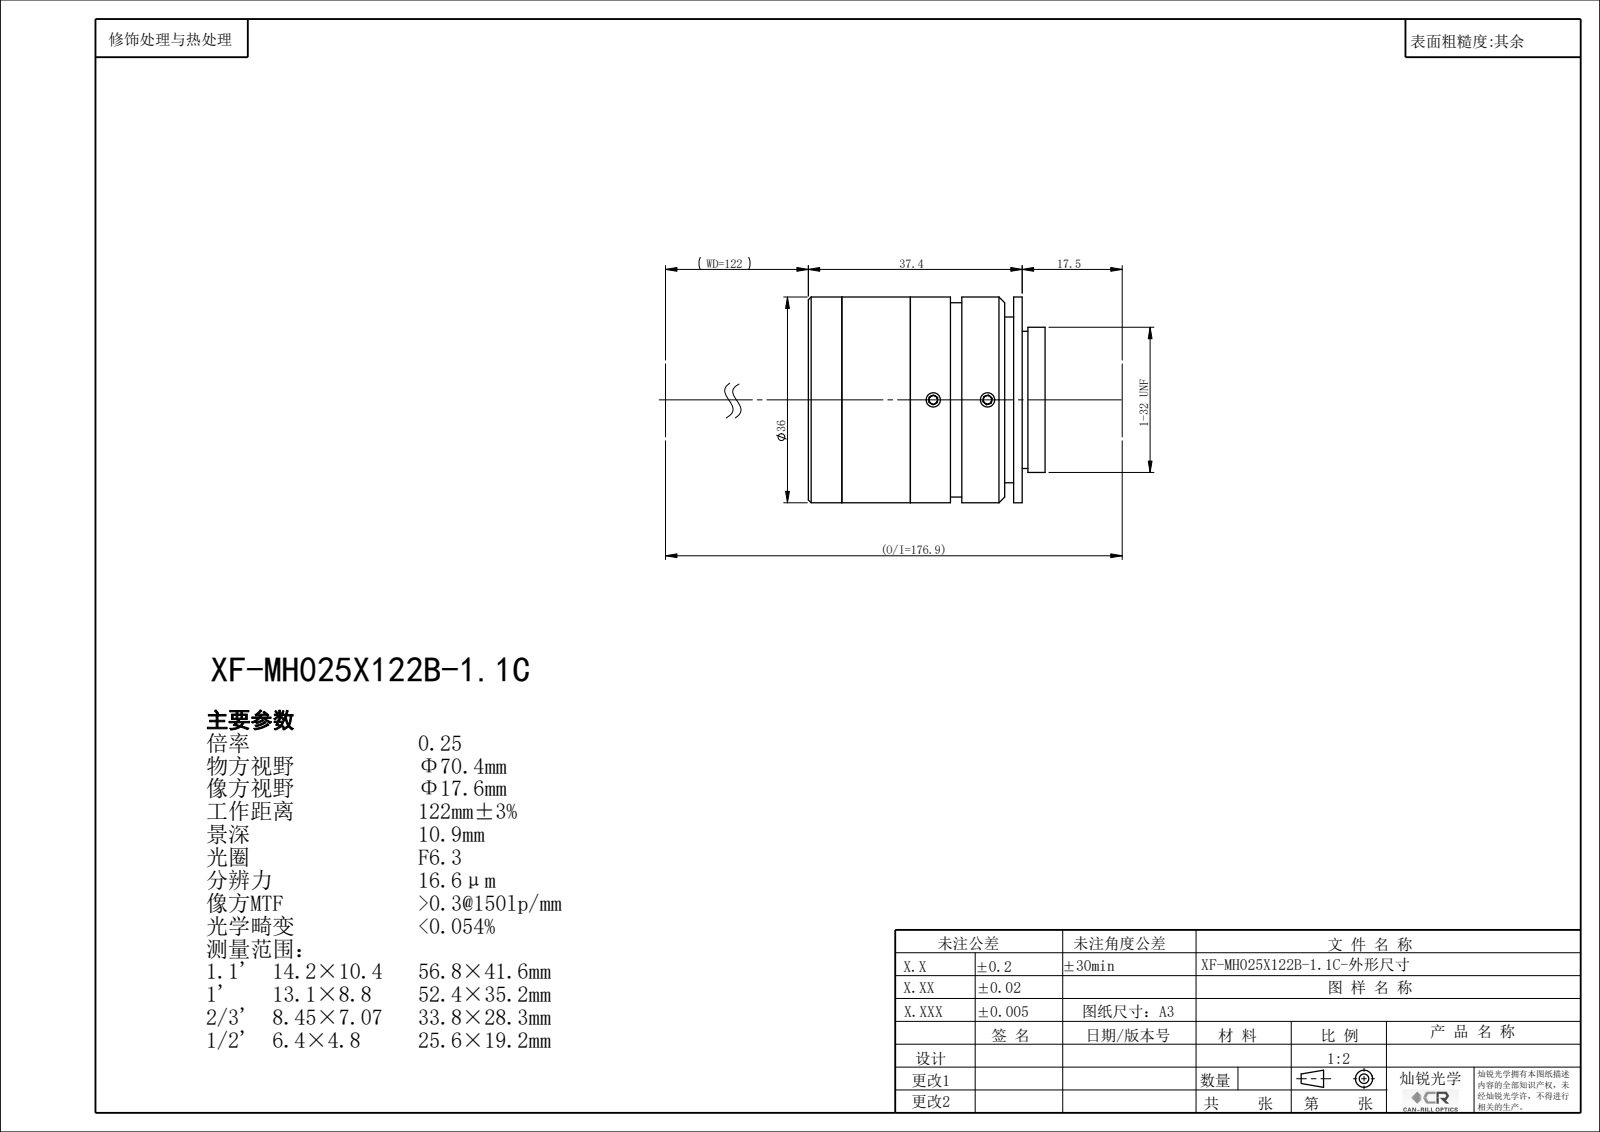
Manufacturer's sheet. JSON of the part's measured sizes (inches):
{"part_name": "XF-MH025X122B-1.1C", "step_written_by": "SolidWorks 2022 (CONFIG_CONTROL_DESIGN)", "units": "inches", "bodies": {"solids": 0, "faces": 151, "planar": 79, "cylindrical": 44, "other": 28}, "overall_size": [1.632, 1.417, 1.417], "round_holes": [[0.098, 6], [0.551, 1], [0.646, 1], [0.669, 1], [0.724, 1], [0.882, 1], [0.945, 1], [0.98, 1], [1.024, 1]], "round_bosses_or_shafts": [[1.417, 1], [1.339, 1], [1, 1]], "face_to_face_distances": [1.474, 0.059, 1.415, 0.231, 1.184, 1.243, 0.177, 0.054, 1.238, 1.297], "hole_center_spacings": [0.374]}
